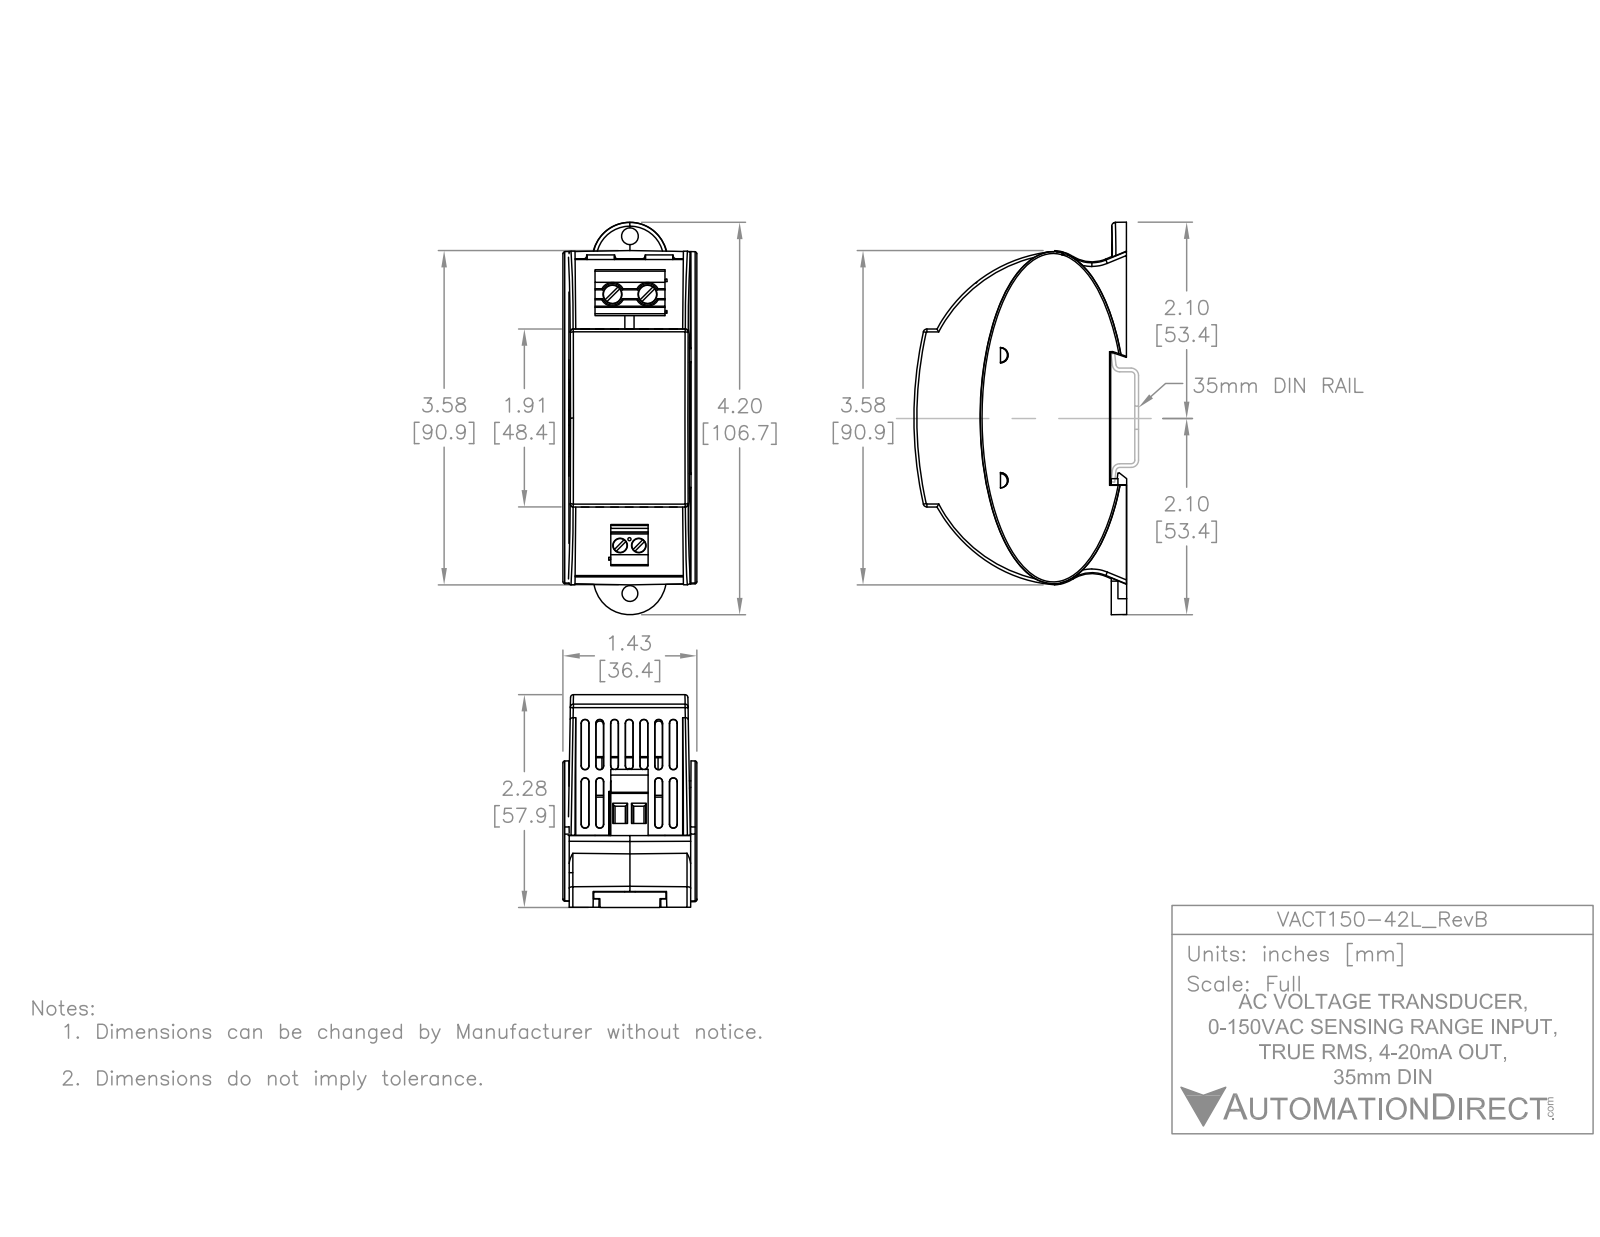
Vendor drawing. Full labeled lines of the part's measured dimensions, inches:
Part name (STEP PRODUCT): VACT150-42L
STEP written by: SolidWorks 2021 (AUTOMOTIVE_DESIGN)
Units: inches
Bodies: 6 solids, 755 faces (442 planar, 122 cylindrical, 191 other)
Overall size (bounding box): 4.203 × 2.279 × 1.435
Volume: 3.085 in³ · Surface area: 76.54 in²
Round holes (diameter × count): ⌀0.157 ×2, ⌀0.205 ×2
Round bosses / shafts (diameter × count): ⌀0.197 ×2, ⌀0.15 ×2, ⌀0.051 ×2, ⌀0.018 ×2
Partial cylindrical surfaces — rounded edges, fillets, slot ends (radius × count): R0.006 ×20, R0.02 ×11, R0.008 ×8, R0.026 ×8, R0.039 ×8, R0.012 ×4, R0.032 ×4, R0.04 ×4
Main face-to-face distances: 1.435, 0.064, 0.5, 0.436, 0.702, 0.266, 0.766, 1.271, 1.257, 0.067
Hole centre spacings: 0.2, 0.375, 2.69, 2.691, 2.704, 2.705
